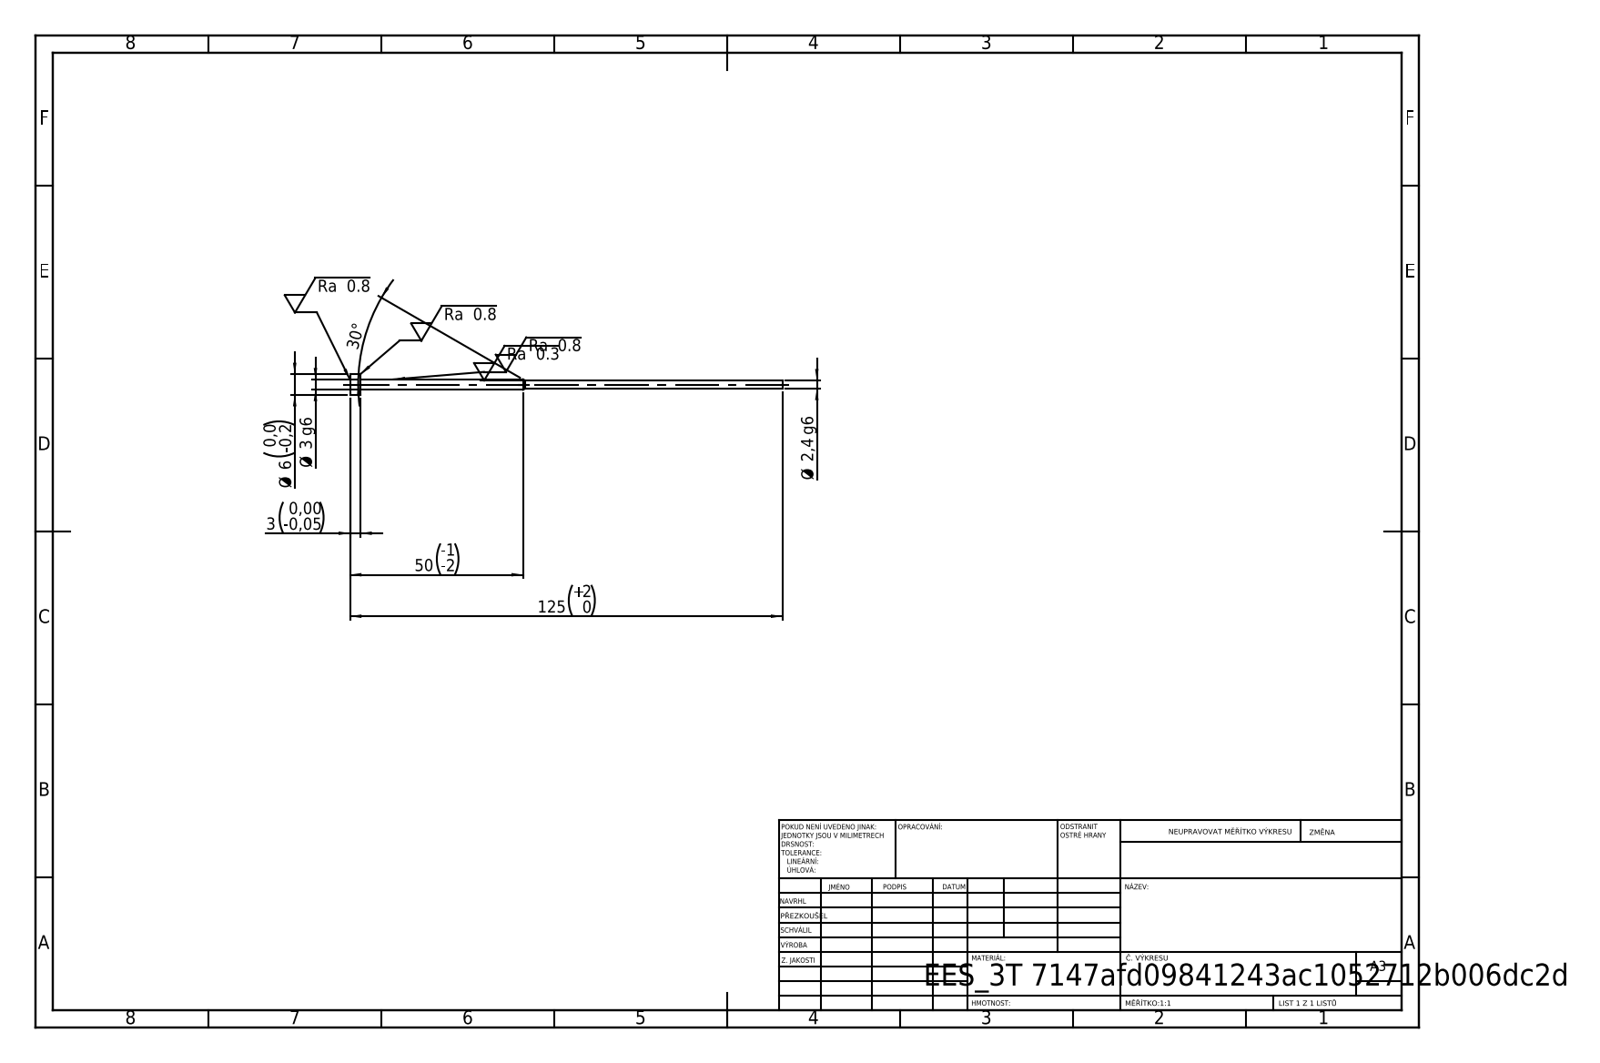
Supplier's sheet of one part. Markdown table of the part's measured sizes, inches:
| quantity | value |
| --- | --- |
| STEP written by | SolidWorks 2019 (CONFIG_CONTROL_DESIGN) |
| units | inches |
| bodies | 1 solid, 11 faces (3 planar, 6 cylindrical, 2 other) |
| overall size | 4.921 × 0.236 × 0.236 |
| volume | 0.046 in³ |
| surface area | 1.736 in² |
| round bosses / shafts (diameter × count) | 0.236 × 1, 0.118 × 1, 0.094 × 1 |
| main face-to-face distances | 0.118, 4.803, 4.921 |
